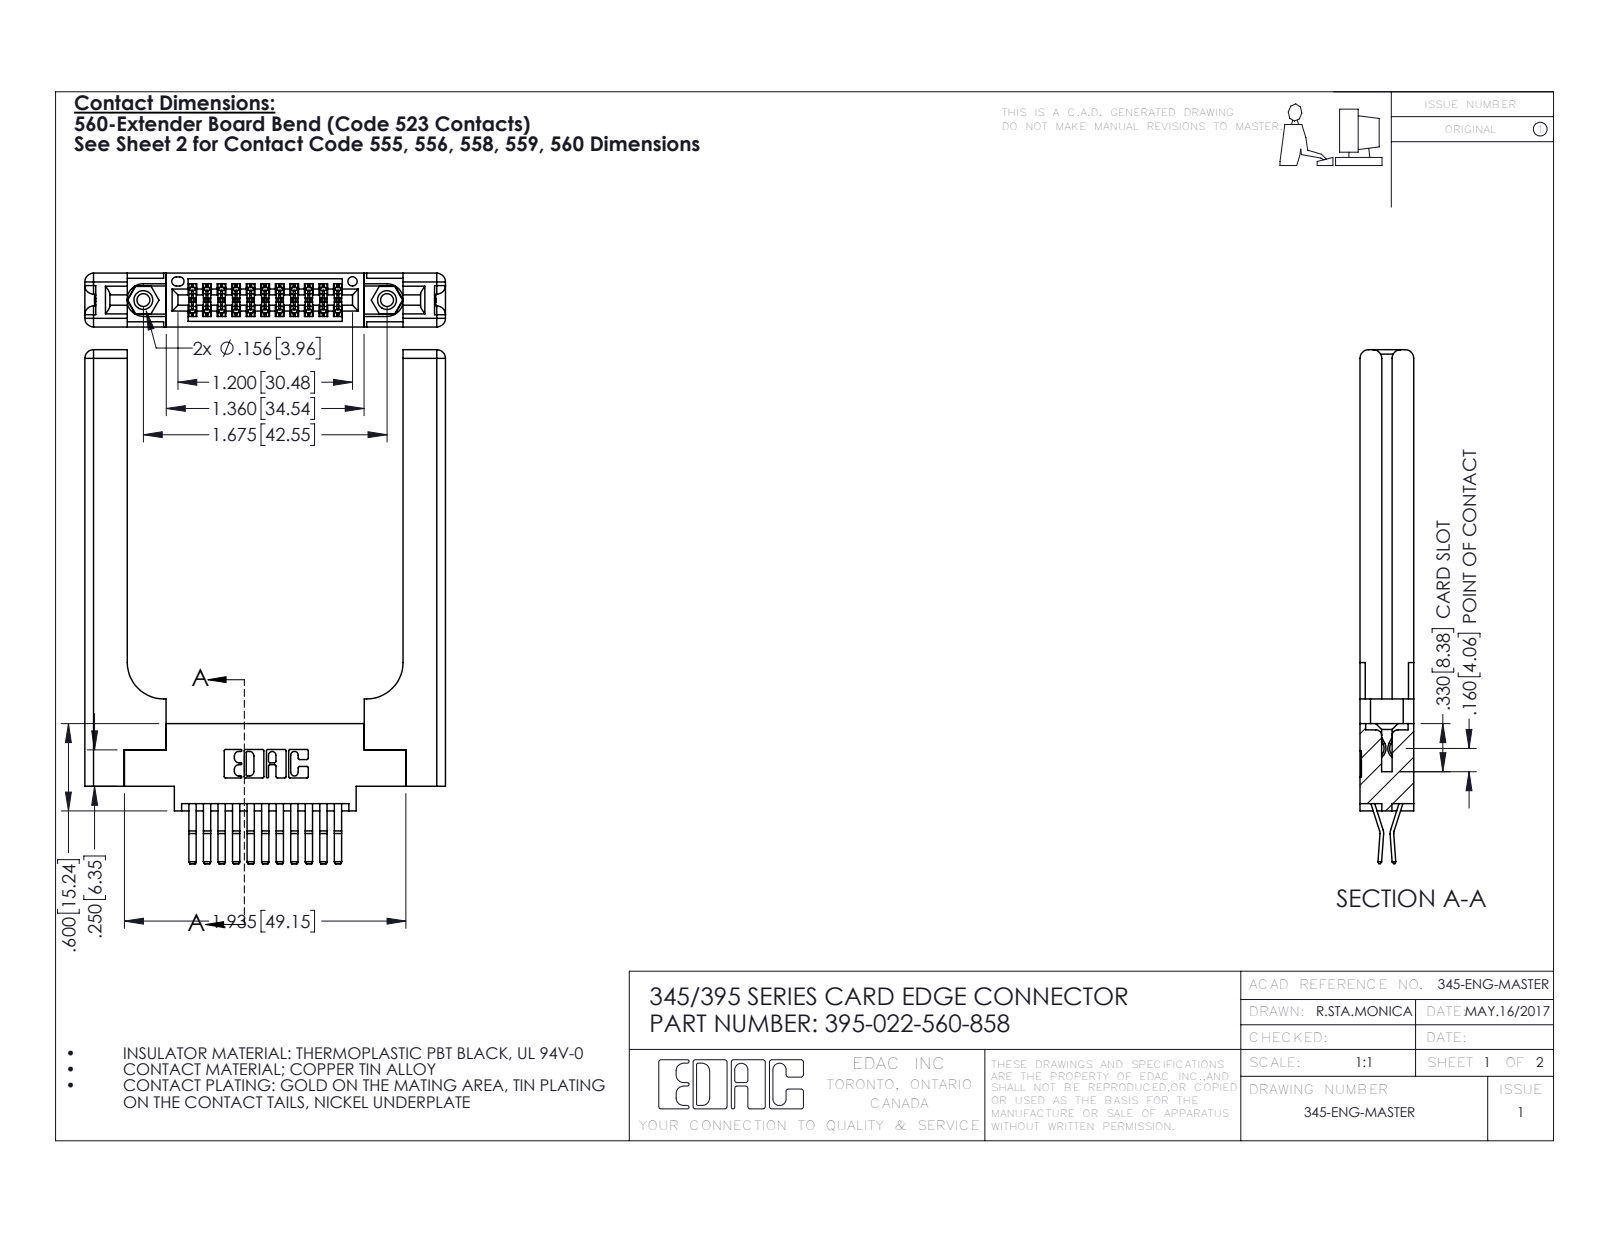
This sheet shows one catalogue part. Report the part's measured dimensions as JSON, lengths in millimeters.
{"part_name": "345-220-058_345-220-058; 345 Part_0.170 Offset - 0.156 Dia-TH; 345-250-001_345-250-001-102; 395-022-560-858 (+1 more)", "step_written_by": "SolidWorks 2016 (CONFIG_CONTROL_DESIGN)", "units": "millimeters", "bodies": {"solids": 27, "faces": 1530, "planar": 958, "cylindrical": 512, "other": 60}, "overall_size": [89.7, 63, 9.4], "volume_mm3": 14300, "surface_area_mm2": 13630, "round_holes": [[2.3, 2], [3.2, 2], [4, 2], [1.6, 1]], "round_bosses_or_shafts": [[3.9, 2]], "partial_cylinders_radius": [[0.2, 33], [0.3, 22], [1.5, 16], [0.2, 6], [0.8, 6], [0.7, 3], [0.3, 2], [0.4, 2]], "face_to_face_distances": [9.4, 1.8, 3.8, 3.8, 2, 5.6, 7.6, 0.6, 48.2, 5.7], "hole_center_spacings": [6.9, 36.7, 42.5]}
